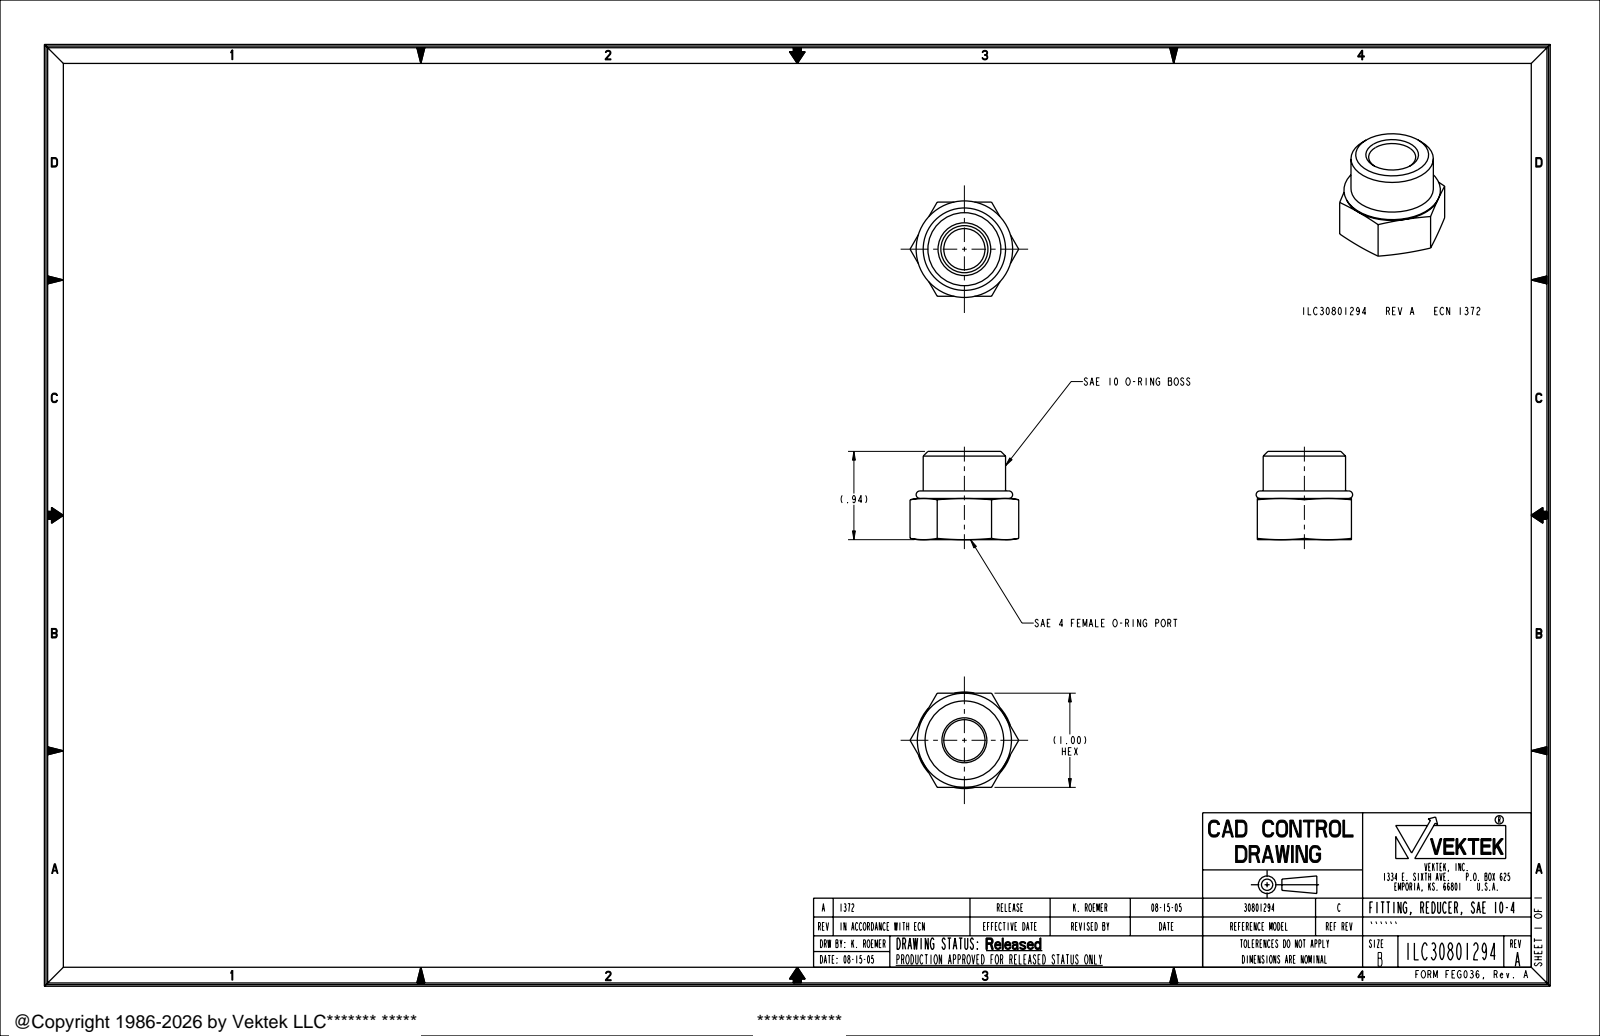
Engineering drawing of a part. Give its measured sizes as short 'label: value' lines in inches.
name: ILC30801294
written by: PRO/ENGINEER BY PARAMETRIC TECHNOLOGY CORPORATION, 2004290 (AUTOMOTIVE_DESIGN_CC2)
unit: in
bodies: 1 solid, 41 faces (11 planar, 10 cylindrical, 20 other)
size: 1.155 × 1.025 × 0.938
volume: 0.52 in³; area: 6.09 in²
holes: 1× ⌀0.437, 1× ⌀0.5, 1× ⌀0.835
bosses: 1× ⌀0.875
face distances: 1, 0.437, 0.428, 0.937, 0.928, 0.5
